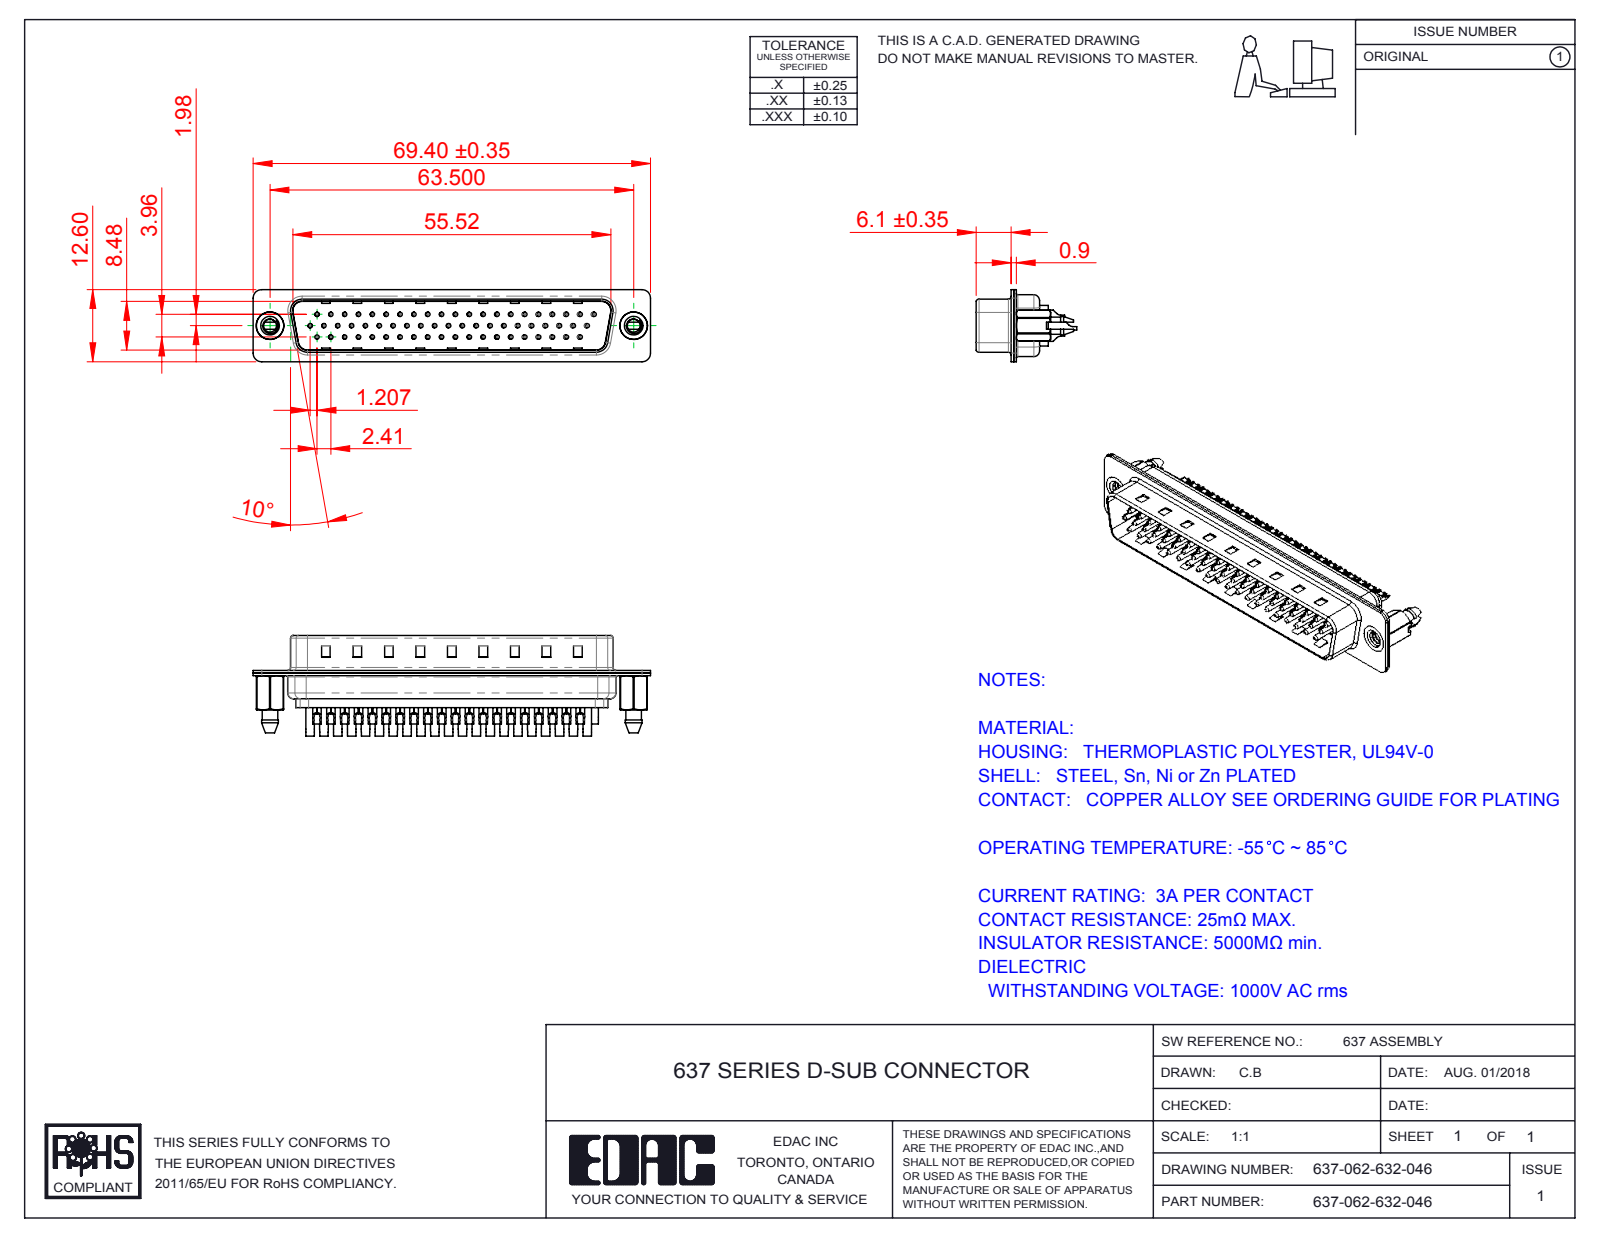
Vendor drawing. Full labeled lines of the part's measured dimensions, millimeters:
Part name (STEP PRODUCT): 637 Housing_62 Contacts; 637 Shell Front_62 Contacts; 637 Contact Row 2_32; 637-062-632-046 (+4 more)
STEP written by: SolidWorks 2016 (CONFIG_CONTROL_DESIGN)
Units: millimetres
Bodies: 67 solids, 4454 faces (1103 planar, 1971 cylindrical, 1380 other)
Overall size (bounding box): 69.4 × 17.55 × 12.6
Volume: 3 863 mm³ · Surface area: 14 458 mm²
Round holes (diameter × count): ⌀1.6 ×119, ⌀0.35 ×62, ⌀1.1 ×62, ⌀0.75 ×57, ⌀2 ×57, ⌀2.26 ×2, ⌀4 ×2, ⌀4.8 ×2
Round bosses / shafts (diameter × count): ⌀2 ×62, ⌀1.5 ×62, ⌀0.75 ×62, ⌀4.9 ×2
Partial cylindrical surfaces — rounded edges, fillets, slot ends (radius × count): R1.5 ×18, R2 ×12, R0.5 ×8, R1 ×7, R1.6 ×6, R0.25 ×4, R0.55 ×4, R0.7 ×4
Main face-to-face distances: 0.45, 0.4, 0.7, 8.88, 8.48, 0.9, 0.31, 0.76, 1.16, 0.71
Hole centre spacings: 7.24, 2.32, 2.41, 4.13, 9.65, 4.83, 14.48, 11.04
